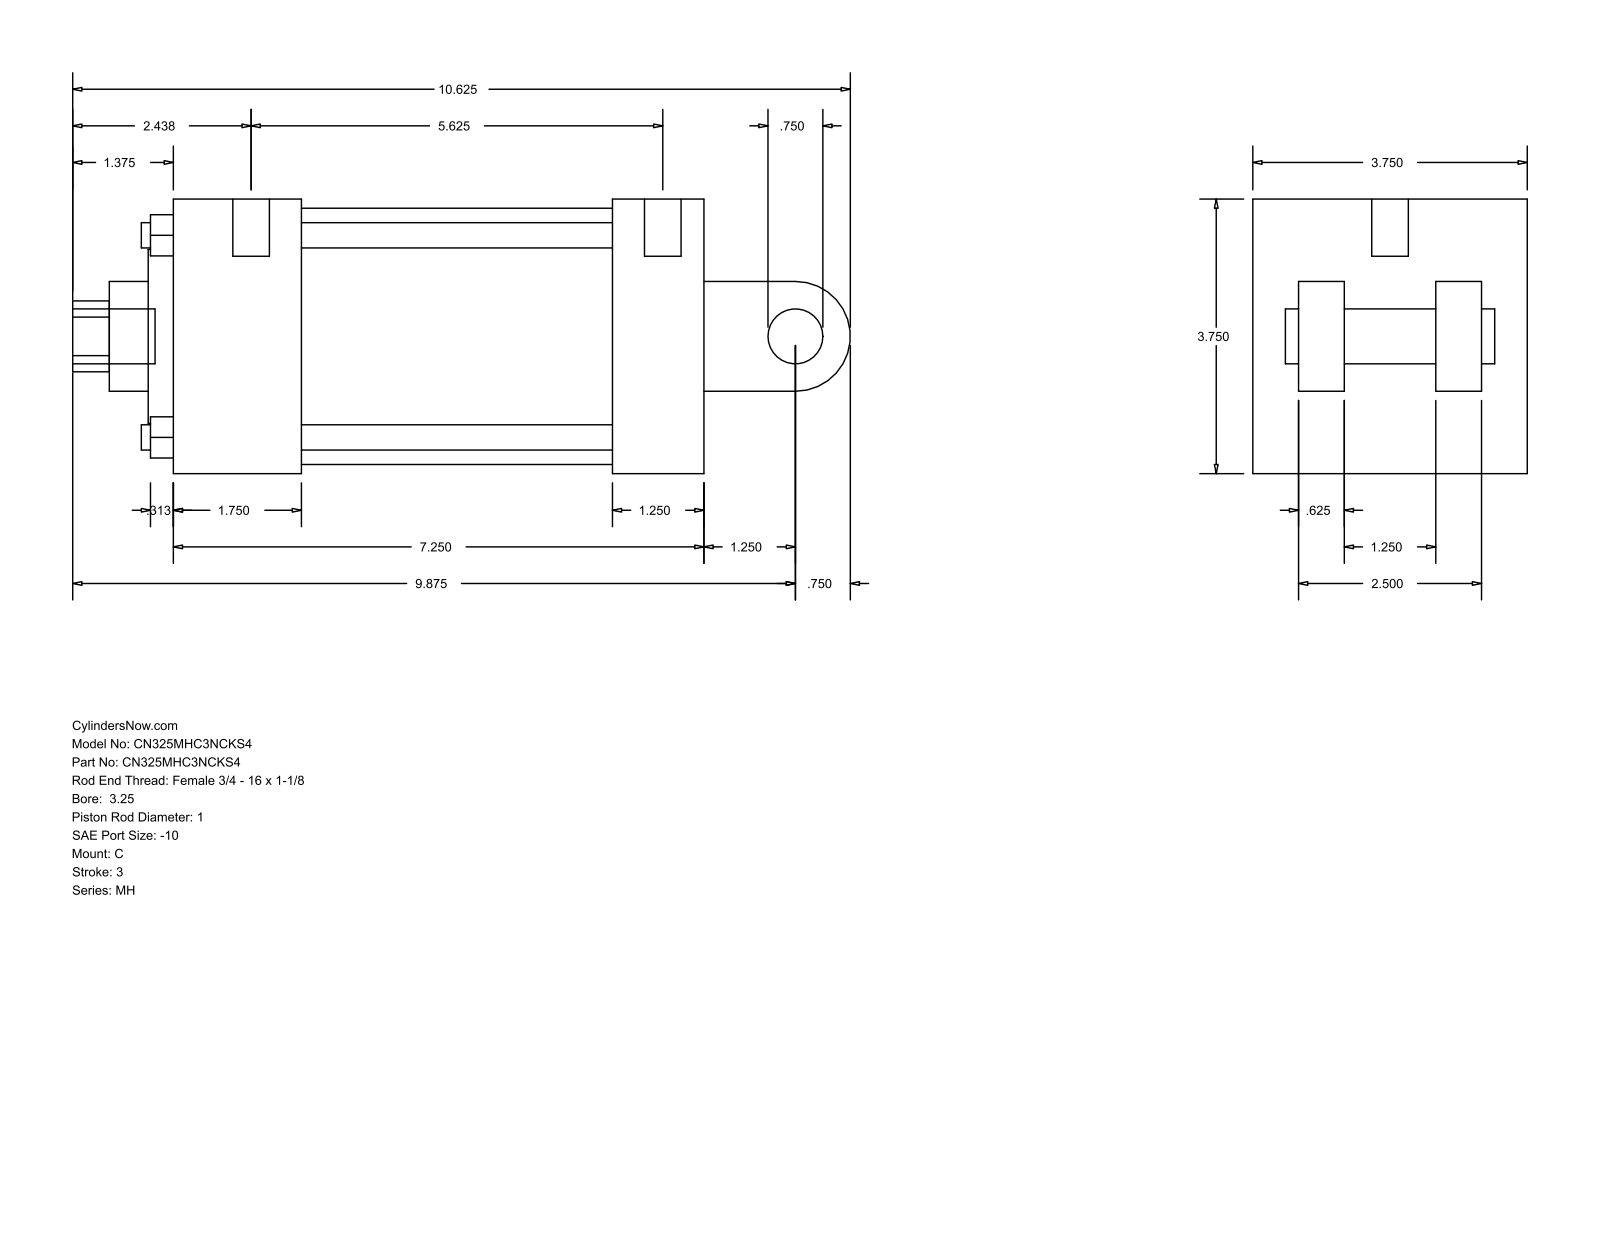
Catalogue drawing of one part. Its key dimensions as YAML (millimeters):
part_name: "MH_C__0325_1"
step_written_by: "GSSL Pune (CONFIG_CONTROL_DESIGN)"
units: millimeters
bodies: {solids: 0, faces: 101, planar: 71, cylindrical: 30, other: 0}
overall_size: [269.88, 95.25, 95.25]
round_holes:
  - {diameter: 8.76, count: 4}
  - {diameter: 5.56, count: 2}
  - {diameter: 12.7, count: 1}
  - {diameter: 25.4, count: 1}
  - {diameter: 38.1, count: 1}
  - {diameter: 60.33, count: 1}
  - {diameter: 88.9, count: 1}
round_bosses_or_shafts:
  - {diameter: 19.05, count: 2}
  - {diameter: 5.56, count: 2}
  - {diameter: 12.7, count: 1}
partial_cylinders:
  - {radius: 12.29, count: 1}
  - {radius: 19.05, count: 1}
face_to_face_distances: [95.24, 15.87, 184.15, 63.5, 31.74, 79.37, 47.63, 44.46, 152.4, 107.94]
hole_center_spacings: [49.57, 70.1, 99.14, 4.76]
